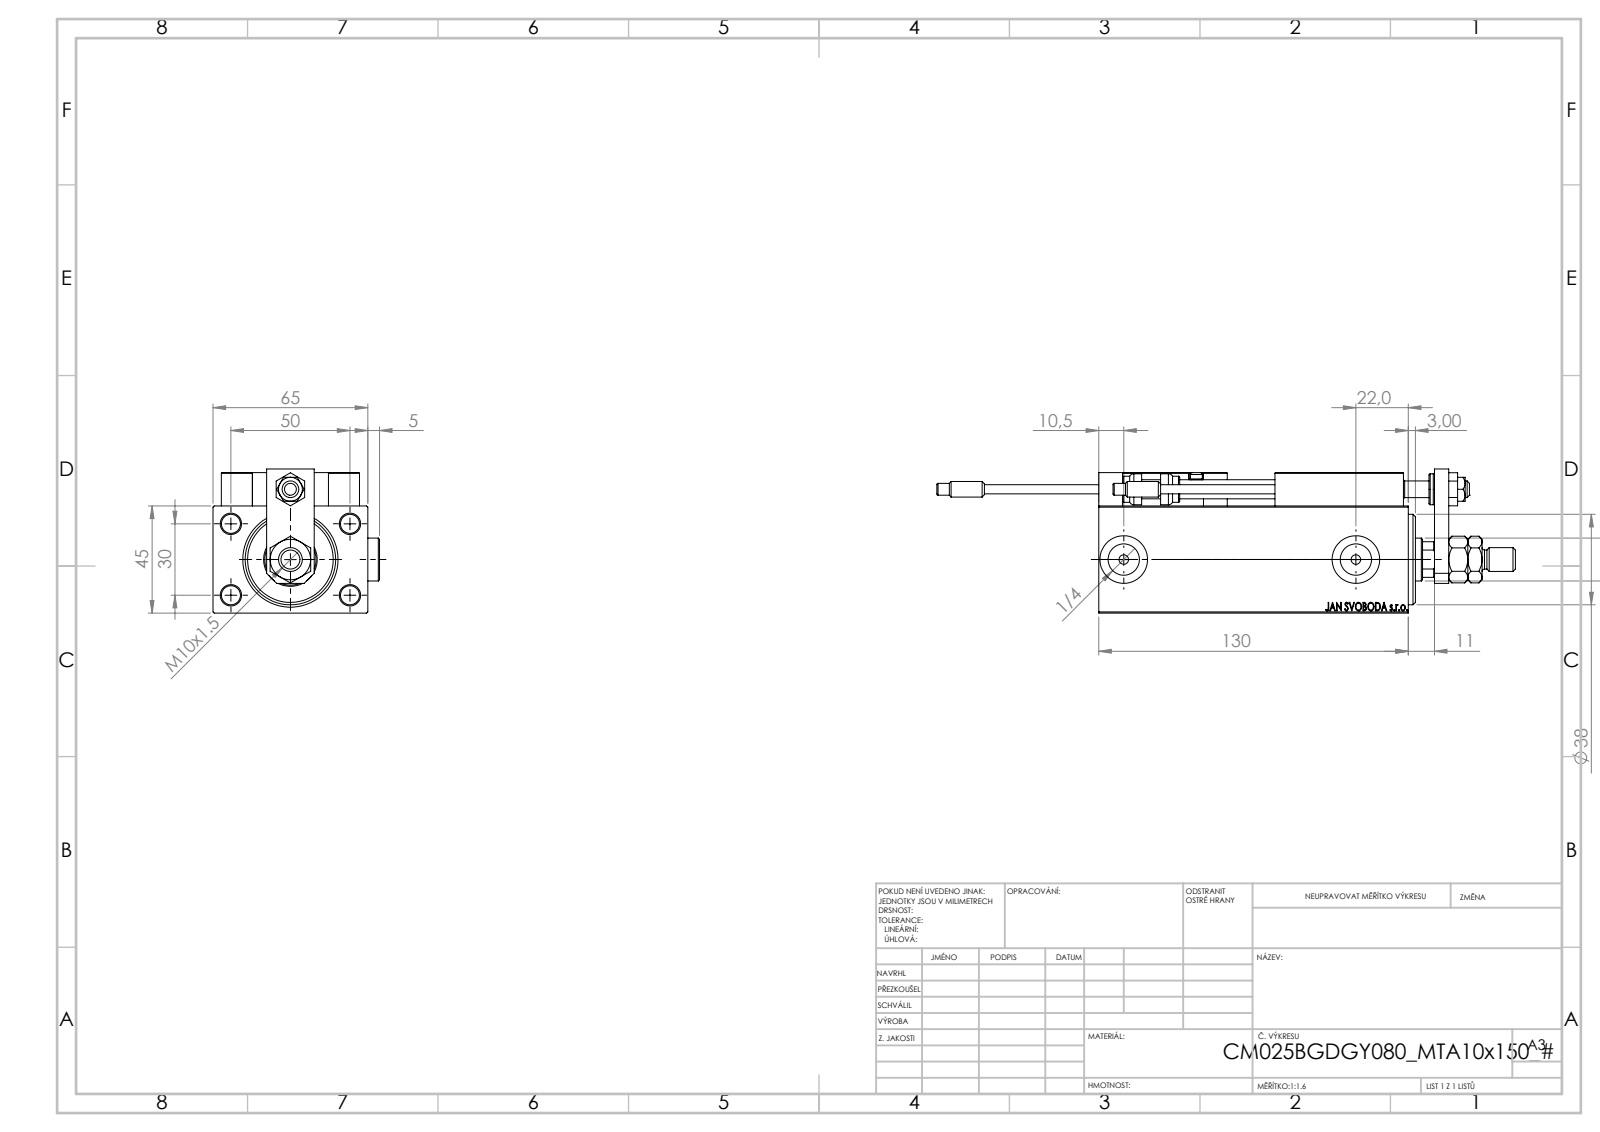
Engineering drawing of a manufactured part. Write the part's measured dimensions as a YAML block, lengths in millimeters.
part_name: "ALLEN BOLT D8; TYC_L79; ALLEN BOLT D5; NUT_D10 (+7 more)"
step_written_by: "SolidWorks 2019 (CONFIG_CONTROL_DESIGN)"
units: millimeters
bodies: {solids: 27, faces: 1443, planar: 612, cylindrical: 212, other: 619}
overall_size: [243, 69.9, 60.5]
volume: 407441
surface_area: 92503
round_holes:
  - {diameter: 8, count: 9}
  - {diameter: 4, count: 6}
  - {diameter: 3.2, count: 4}
  - {diameter: 5, count: 2}
  - {diameter: 13.16, count: 2}
  - {diameter: 20, count: 2}
  - {diameter: 7, count: 1}
  - {diameter: 8.5, count: 1}
  - {diameter: 14.5, count: 1}
  - {diameter: 18, count: 1}
  - {diameter: 21.5, count: 1}
  - {diameter: 22.5, count: 1}
round_bosses_or_shafts:
  - {diameter: 5, count: 4}
  - {diameter: 18, count: 2}
  - {diameter: 6.5, count: 2}
  - {diameter: 3.8, count: 2}
  - {diameter: 13, count: 1}
  - {diameter: 11, count: 1}
  - {diameter: 10, count: 1}
  - {diameter: 8, count: 1}
partial_cylinders:
  - {radius: 0.3, count: 30}
  - {radius: 3, count: 2}
  - {radius: 8.5, count: 1}
face_to_face_distances: [45, 65, 14, 6, 59, 5, 13, 141, 3.5, 19]
hole_center_spacings: [29.15, 11.37, 20, 28.9, 29.59, 29.69, 30, 36.06]
